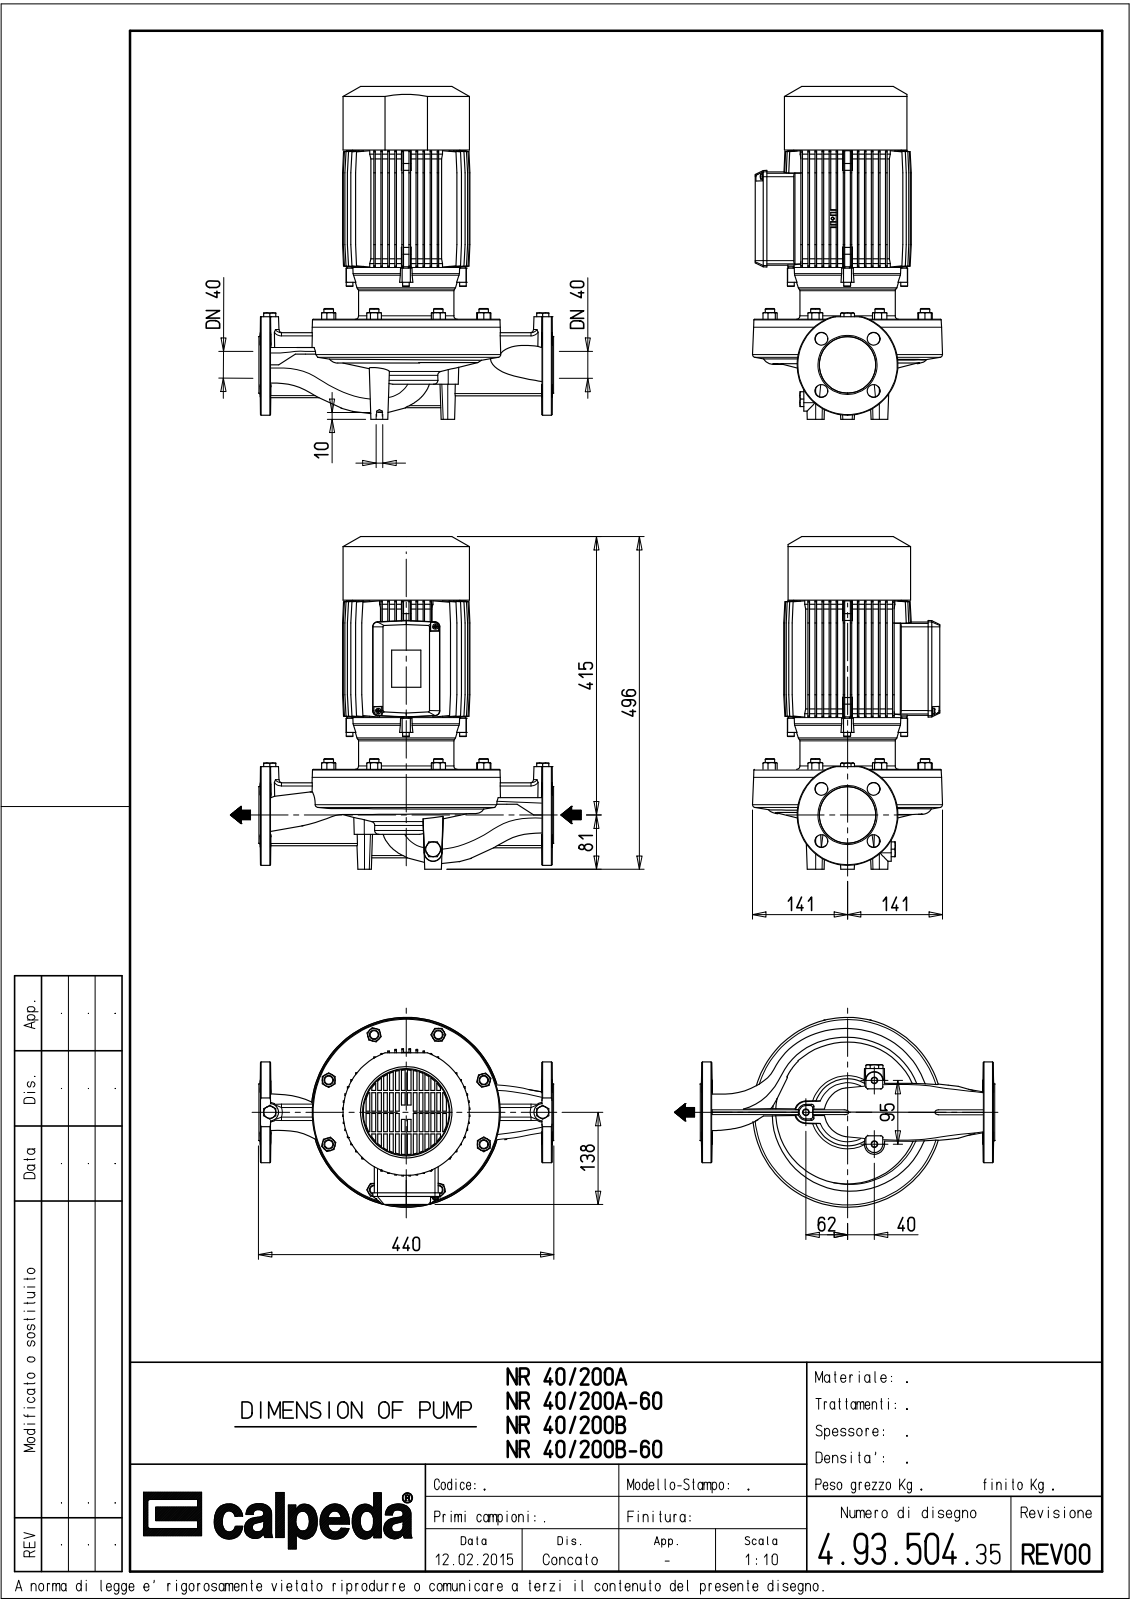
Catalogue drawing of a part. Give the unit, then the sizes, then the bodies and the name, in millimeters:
Units: millimetres
Overall size (bounding box): 496 × 440 × 282.84
Round holes (diameter × count): ⌀19 ×8, ⌀8.5 ×3, ⌀4.4 ×1
Round bosses / shafts (diameter × count): ⌀14 ×8, ⌀10 ×4, ⌀7 ×4, ⌀8 ×2, ⌀188 ×1, ⌀160 ×1, ⌀150 ×1, ⌀142 ×1
Partial cylindrical surfaces — rounded edges, fillets, slot ends (radius × count): R3 ×6, R3.5 ×6, R5 ×6, R50 ×1, R63 ×1, R79 ×1, R89.5 ×1
Main face-to-face distances: 8.8, 17.6, 26.4, 35.2, 3.3, 5.5, 44, 14.3, 12.1, 52.8
Hole centre spacings: 101.98, 112.52, 95
Volume: 13 840 000 mm³ · Surface area: 1 066 000 mm²
Bodies: 1 solid, 1231 faces (830 planar, 137 cylindrical, 264 other)
Part name (STEP PRODUCT): 91463
STEP written by: THINKDESIGN (AUTOMOTIVE_DESIGN)
